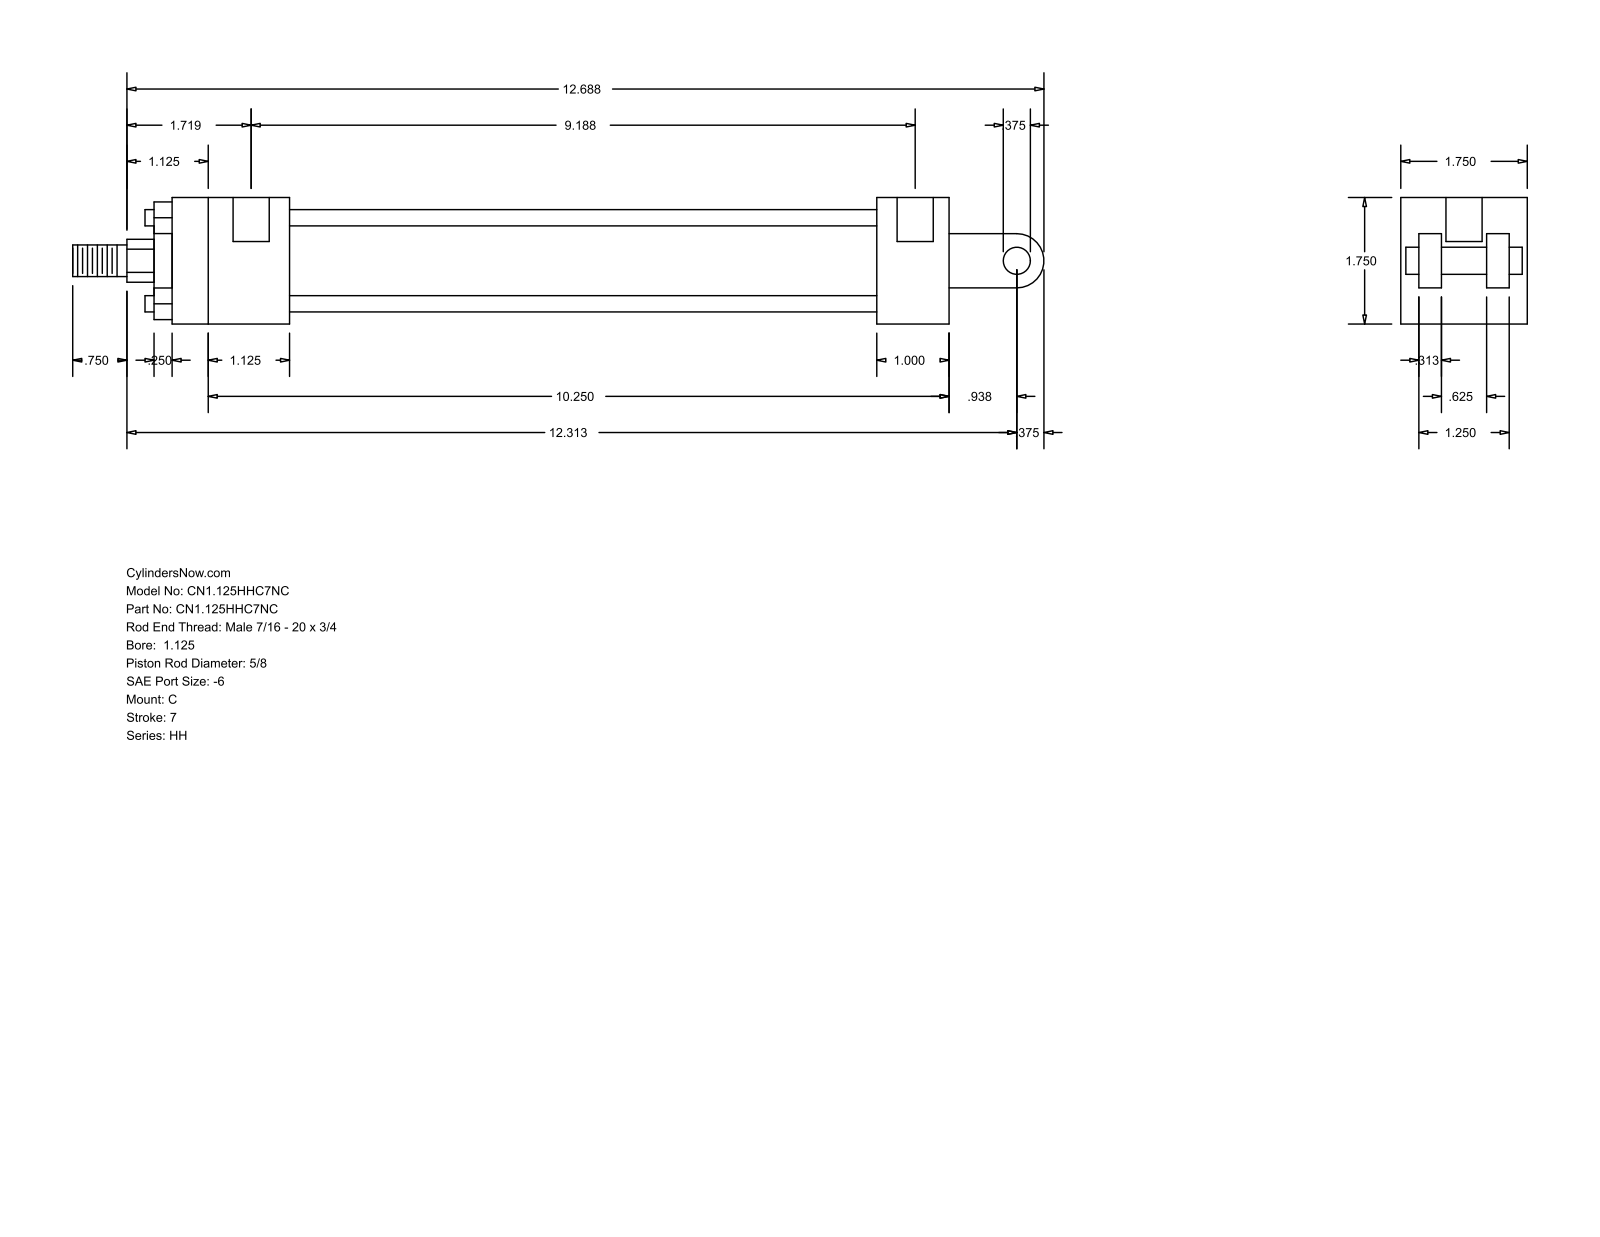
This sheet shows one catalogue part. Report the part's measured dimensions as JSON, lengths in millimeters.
{"part_name": "HH_C__0112_0.625", "step_written_by": "GSSL Pune (CONFIG_CONTROL_DESIGN)", "units": "millimeters", "bodies": {"solids": 0, "faces": 99, "planar": 70, "cylindrical": 29, "other": 0}, "overall_size": [341.31, 44.45, 44.45], "round_holes": [[5.56, 4], [12.7, 2]], "round_bosses_or_shafts": [[5.71, 4], [34.92, 1], [28.57, 1], [15.88, 1], [11.11, 1], [9.53, 1]], "partial_cylinders_radius": [[7.54, 1], [9.53, 1]], "face_to_face_distances": [44.46, 6.35, 31.76, 14.29, 30.17, 38.11, 7.94, 23.82, 41.27, 12.7], "hole_center_spacings": [230.19, 3.17, 233.36]}
